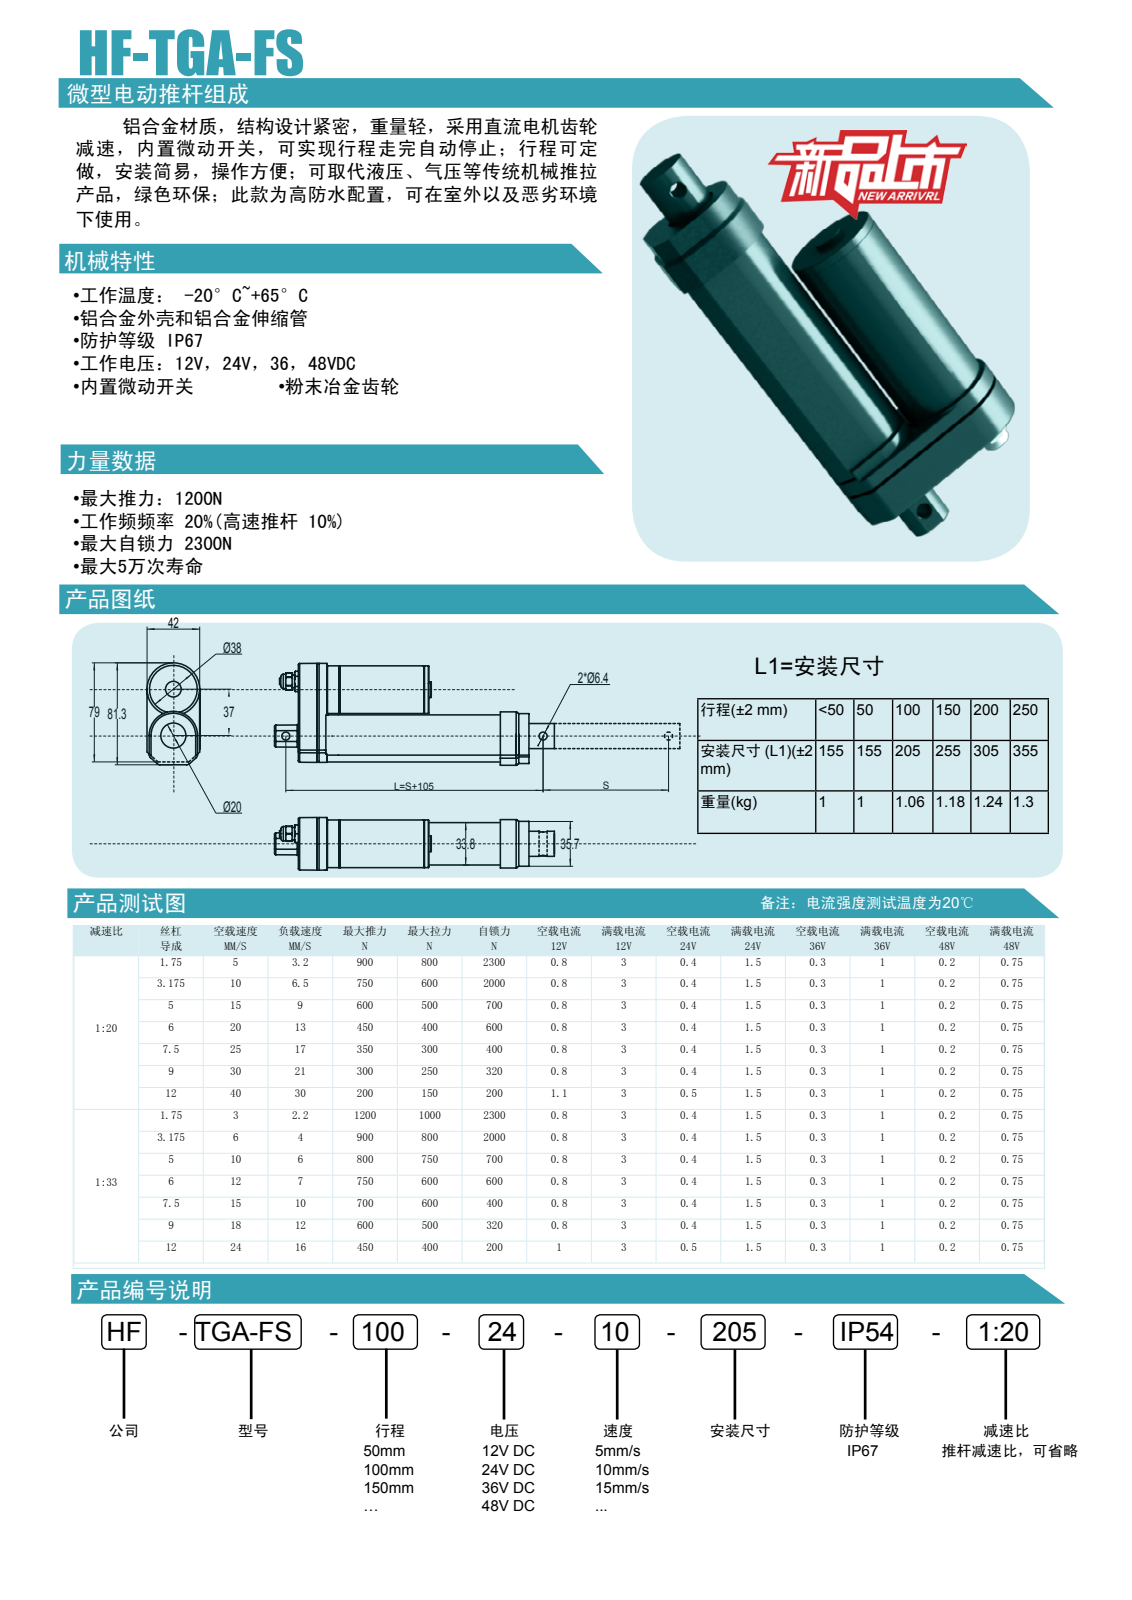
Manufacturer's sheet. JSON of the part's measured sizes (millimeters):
{"part_name": "END; UP; MOTER; WK (+3 more)", "step_written_by": "PRO/ENGINEER BY PARAMETRIC TECHNOLOGY CORPORATION, 2008380 (CONFIG_CONTROL_DESIGN)", "units": "millimeters", "bodies": {"solids": 6, "faces": 200, "planar": 73, "cylindrical": 88, "other": 39}, "overall_size": [224, 81.55, 42], "volume_mm3": 334042, "surface_area_mm2": 79609, "round_holes": [[4.5, 3], [7, 3], [6.4, 2], [20, 1], [38, 1]], "round_bosses_or_shafts": [[41.93, 1], [13, 1]], "partial_cylinders_radius": [[1, 12], [0.5, 9], [0.9, 4], [1.9, 4], [3.3, 4], [4.65, 4], [0.54, 2], [1, 2]], "face_to_face_distances": [6.7, 6.5, 22, 33.8, 15.3, 15.5, 4.1, 37.9, 1, 183], "hole_center_spacings": [18.85, 50.41, 65.85, 16.03, 31, 37.24, 53.27, 205]}
